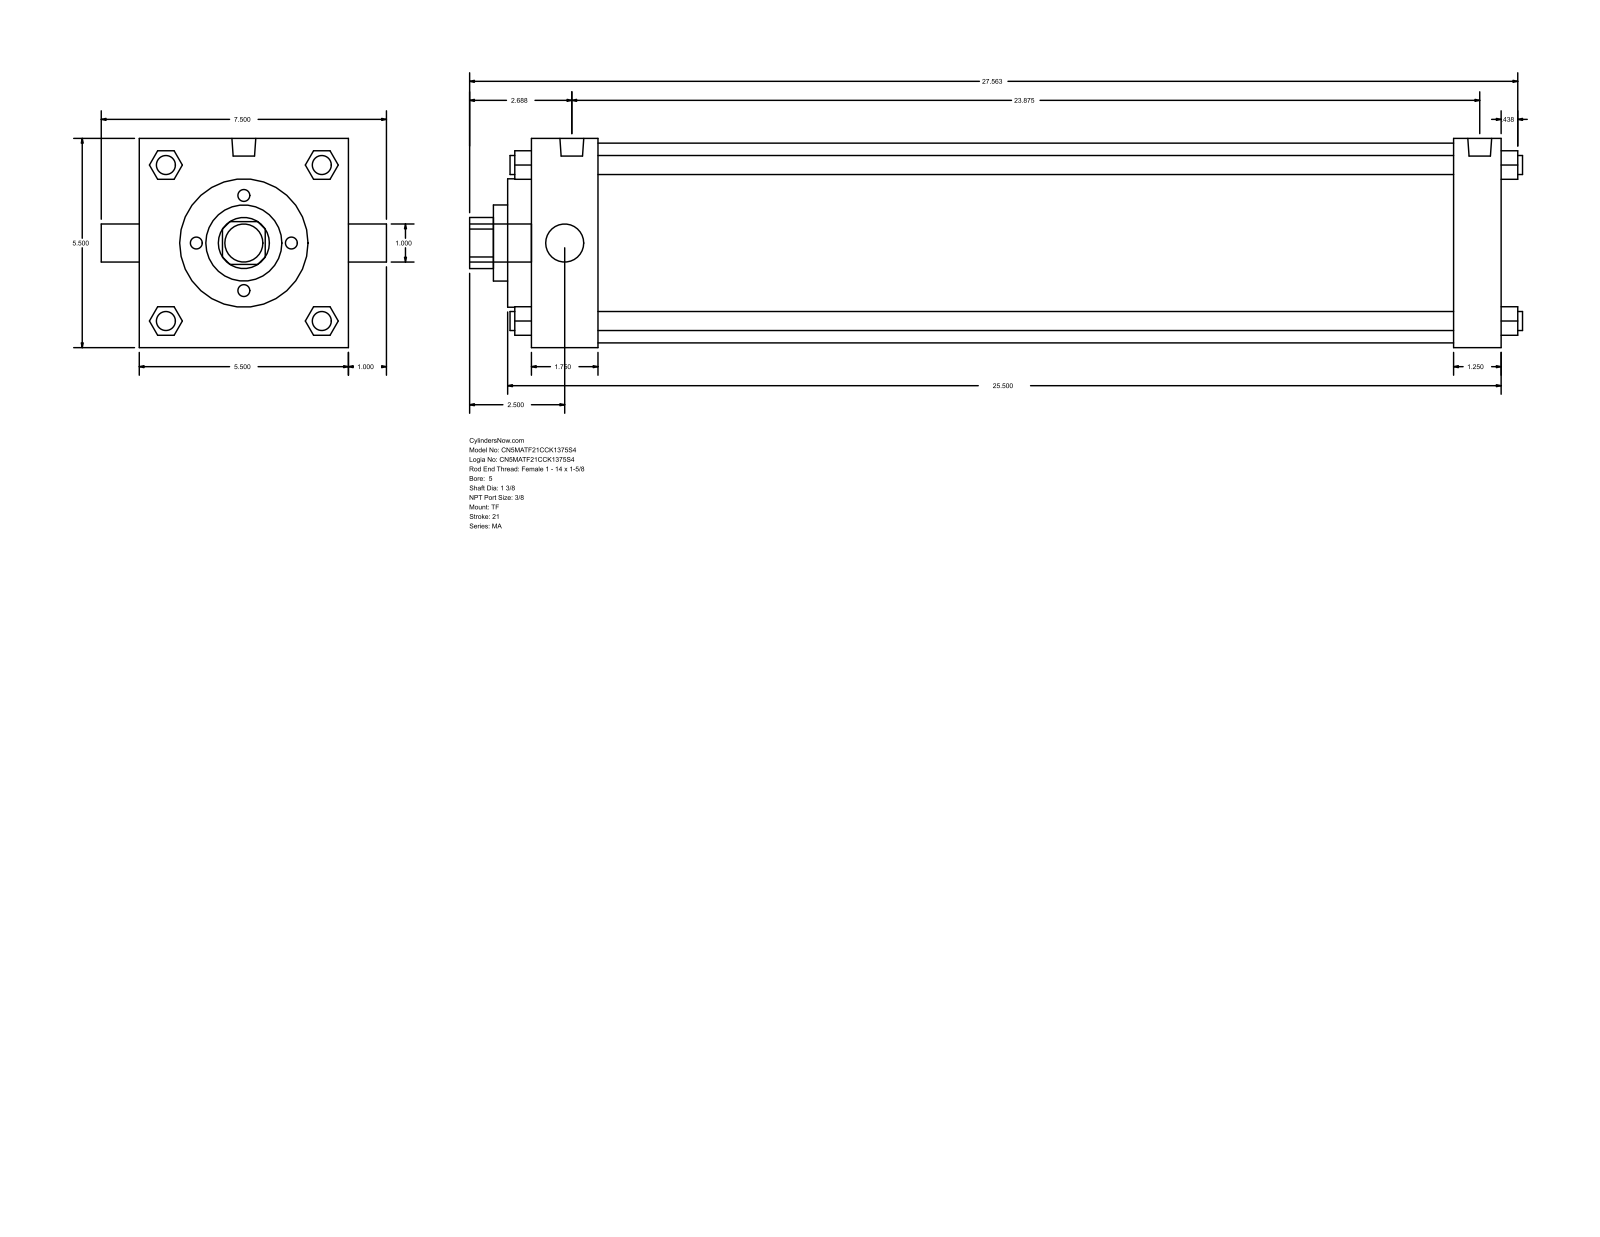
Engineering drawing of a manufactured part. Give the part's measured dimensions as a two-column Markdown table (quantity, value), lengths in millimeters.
| quantity | value |
| --- | --- |
| part name | MA_TF__0500_1.375 |
| STEP written by | GSSL Pune (CONFIG_CONTROL_DESIGN) |
| units | millimeters |
| bodies | 0 solids, 122 faces (93 planar, 29 cylindrical, 0 other) |
| overall size | 703.26 × 190.5 × 139.7 |
| round holes (diameter × count) | 25.4 × 1, 34.92 × 1, 50.8 × 1, 85.72 × 1, 133.35 × 1 |
| round bosses / shafts (diameter × count) | 12.7 × 4, 11.11 × 3, 15.93 × 2, 25.4 × 1 |
| partial cylindrical surfaces (radius × count) | 17.06 × 1 |
| main face-to-face distances | 139.7, 647.71, 615.96, 31.75, 44.45, 571.51, 603.26, 15.87, 60.32, 631.83 |
